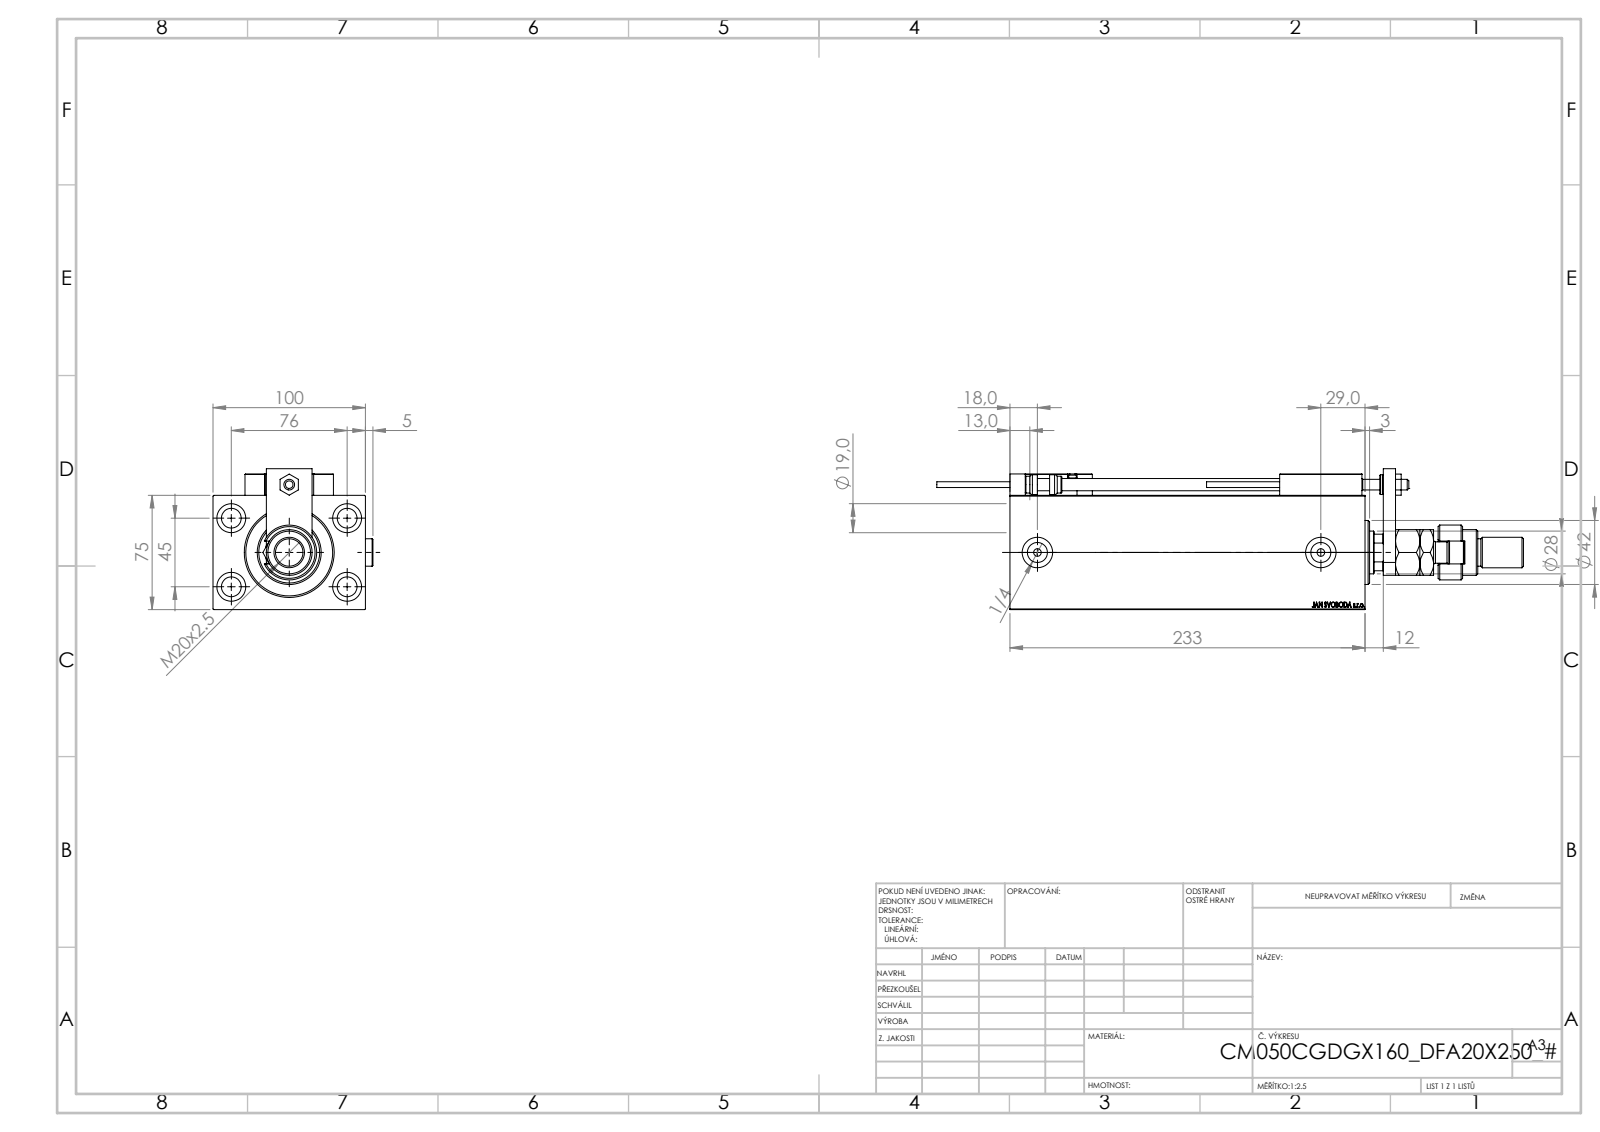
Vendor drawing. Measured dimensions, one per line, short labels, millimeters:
name: ALLEN BOLT D8; SWITCH_X_FRONT_BACK; Zatka_OIL_PORT; V450CM_C_Body (+7 more)
written by: SolidWorks 2019 (CONFIG_CONTROL_DESIGN)
unit: mm
bodies: 27 solids, 1424 faces (623 planar, 219 cylindrical, 582 other)
size: 385 × 104.9 × 92.5
volume: 1 499 000 mm³; area: 254 092 mm²
holes: 5× ⌀8, 4× ⌀3.2, 4× ⌀4, 4× ⌀5, 4× ⌀13, 4× ⌀19, 3× ⌀20, 2× ⌀13.16, 1× ⌀7, 1× ⌀18.5, 1× ⌀28, 1× ⌀31.5
bosses: 3× ⌀18, 2× ⌀5, 2× ⌀3.8, 1× ⌀42, 1× ⌀36, 1× ⌀30, 1× ⌀22, 1× ⌀14
rounds: 30× R0.3, 2× R3, 1× R7.5, 1× R12, 1× R13.5
face distances: 75, 100, 14, 233, 12, 219, 20, 8, 24, 25
hole spacings: 44.16, 11.37, 20, 29.59, 29.69, 36.06, 42.19, 43.91
